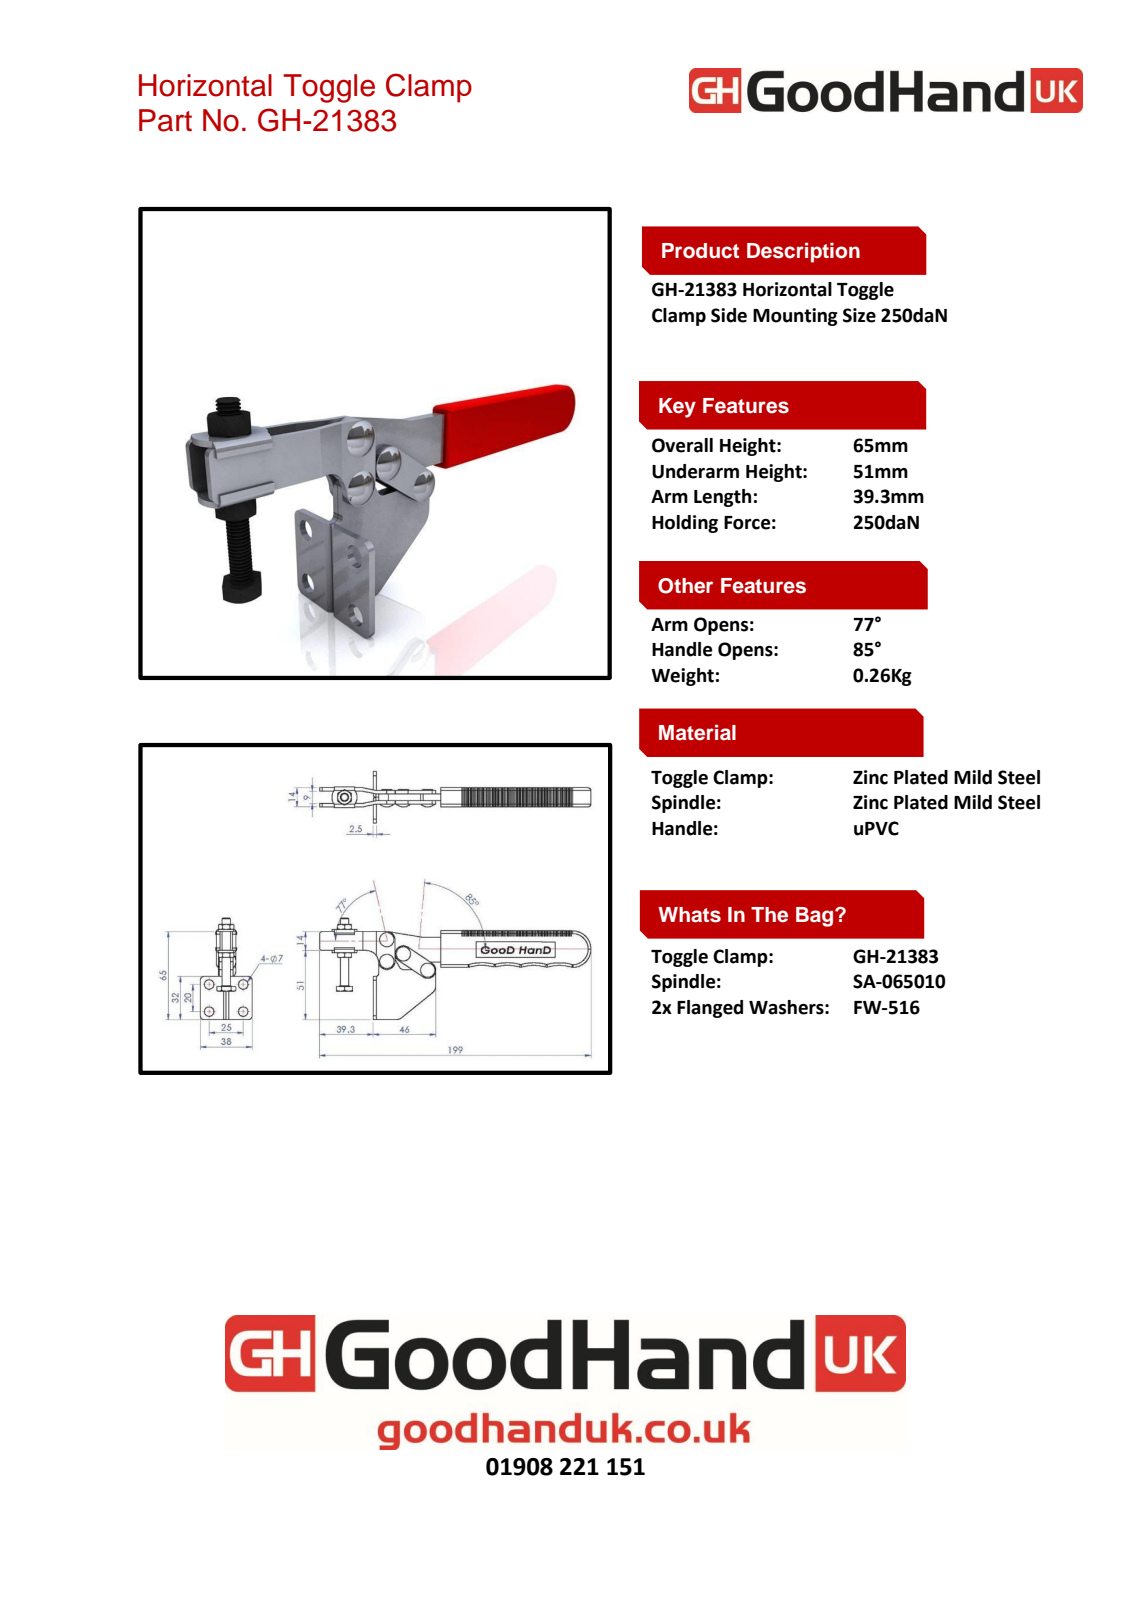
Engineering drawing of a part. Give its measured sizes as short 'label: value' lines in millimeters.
name: Group5^GH-21383(簡化); Group1^GH-21383(簡化); Group4^GH-21383(簡化); GH-21383(簡化) (+2 more)
written by: SolidWorks 2016 (AUTOMOTIVE_DESIGN)
unit: mm
bodies: 5 solids, 271 faces (121 planar, 104 cylindrical, 46 other)
size: 199 × 74.9 × 38
volume: 63 646 mm³; area: 27 257 mm²
holes: 5× ⌀5, 4× ⌀7, 1× ⌀6.33
bosses: 1× ⌀12, 1× ⌀7.5, 1× ⌀6.3, 1× ⌀6
rounds: 11× R3, 4× R1, 4× R2.6, 4× R32, 3× R2, 3× R6, 2× R7, 1× R9
face distances: 9.5, 4.5, 14, 2.5, 5, 2, 12, 7.5, 11.5, 7
hole spacings: 20, 25, 32.02, 13.37, 16, 16.07, 21.49, 30.7
